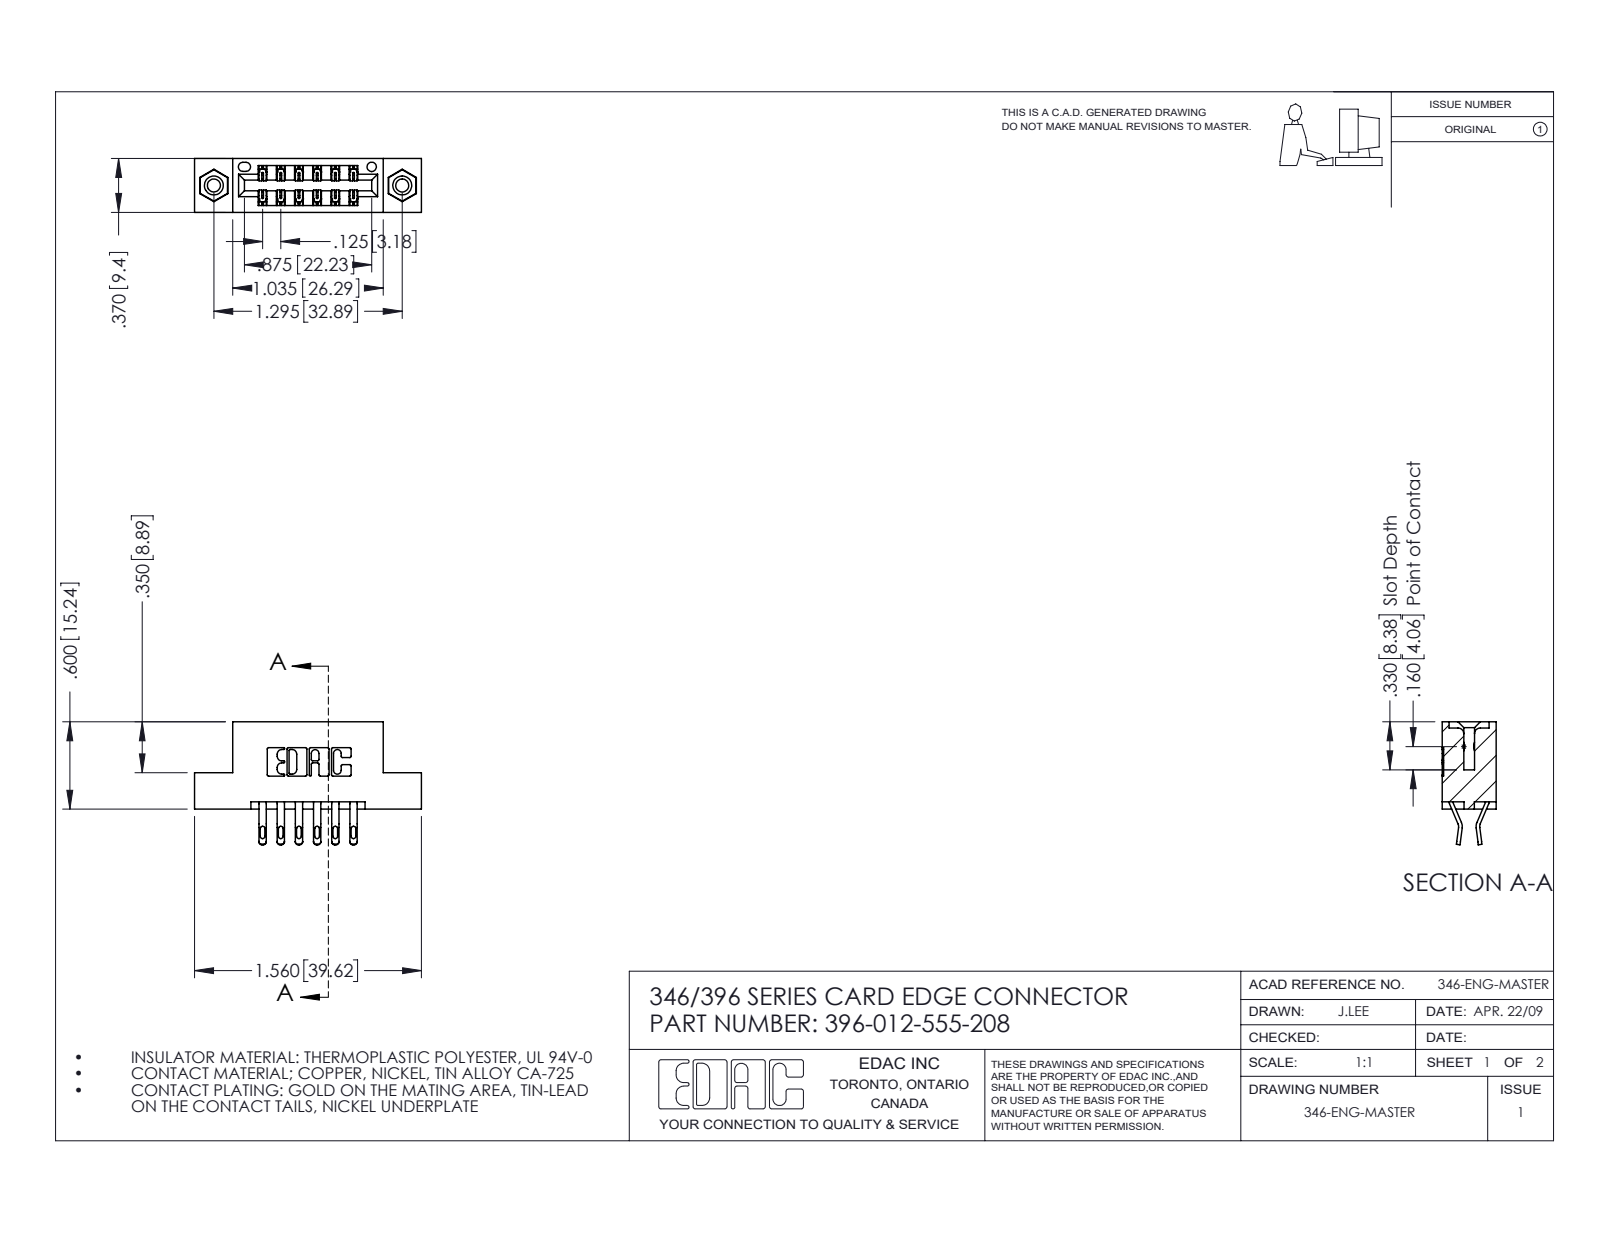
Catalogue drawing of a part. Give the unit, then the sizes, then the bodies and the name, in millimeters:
Units: millimetres
Overall size (bounding box): 39.6 × 21.5 × 9.4
Round holes (diameter × count): ⌀2.3 ×2, ⌀3.2 ×2, ⌀4 ×2, ⌀1.6 ×1
Round bosses / shafts (diameter × count): ⌀3.9 ×2
Partial cylindrical surfaces — rounded edges, fillets, slot ends (radius × count): R0.4 ×24, R0.5 ×24, R0.3 ×22, R0.2 ×18, R0.2 ×6, R0.8 ×6, R0.7 ×3, R0.3 ×2
Main face-to-face distances: 6.4, 9.4, 1.2, 8.2, 3.2, 3.8, 5.6, 2.5, 4.4, 0.6
Hole centre spacings: 6.2, 27.7, 32.9
Volume: 3 610 mm³ · Surface area: 4 544 mm²
Bodies: 15 solids, 878 faces (504 planar, 358 cylindrical, 16 other)
Part name (STEP PRODUCT): 345-250-001_345-250-003-102; 396-012-555-208; 346 Part_Flush Mounting Lugs - 0.156 Dia-TI; 345-292-001_555 Tail
STEP written by: SolidWorks 2016 (CONFIG_CONTROL_DESIGN)
